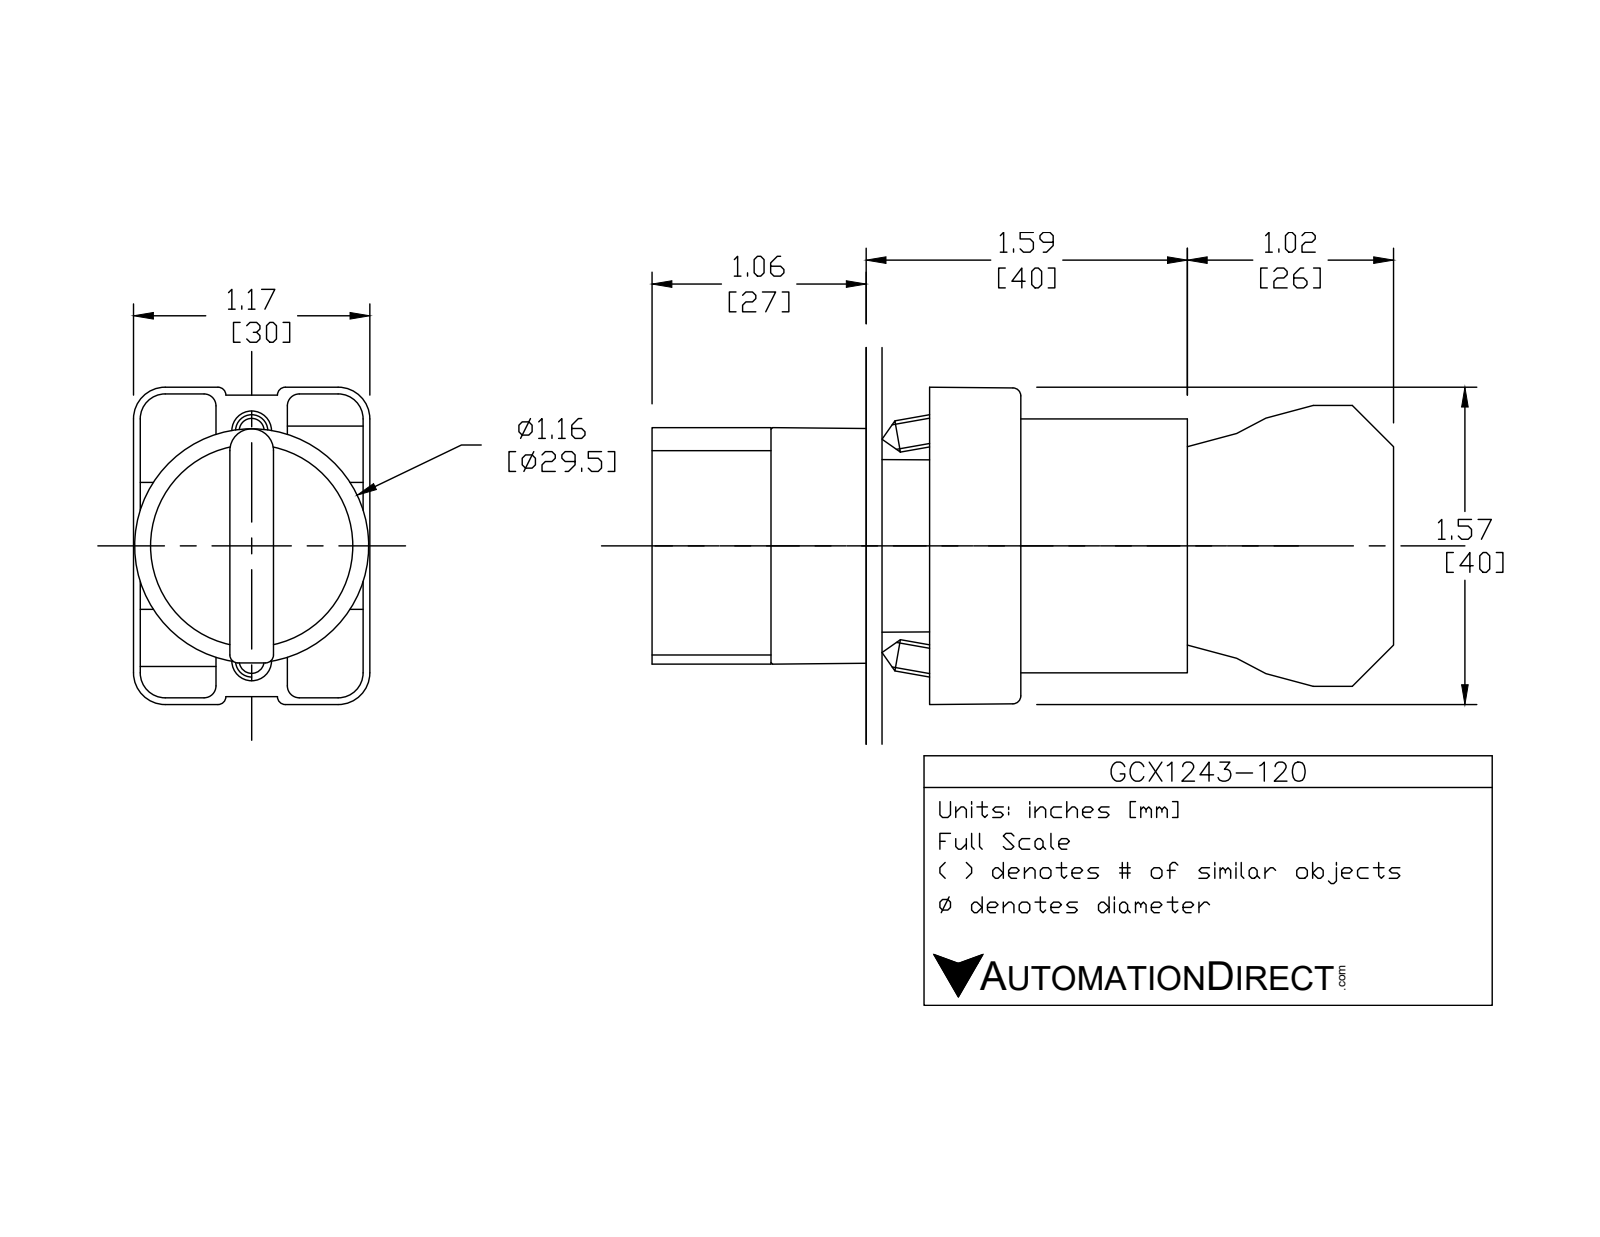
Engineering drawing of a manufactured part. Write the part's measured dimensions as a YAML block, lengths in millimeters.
part_name: "ecx1040; ecx1029; GCX1243-120; GCX1243 OPERATOR (+1 more)"
step_written_by: "SolidWorks 2016 (AUTOMOTIVE_DESIGN)"
units: millimeters
bodies: {solids: 8, faces: 445, planar: 263, cylindrical: 151, other: 31}
overall_size: [92.8, 40.2, 29.9]
volume: 45870
surface_area: 25160
round_holes:
  - {diameter: 2, count: 2}
  - {diameter: 3.1, count: 2}
  - {diameter: 3.3, count: 2}
  - {diameter: 2.2, count: 1}
  - {diameter: 5, count: 1}
  - {diameter: 11.9, count: 1}
  - {diameter: 22.3, count: 1}
  - {diameter: 22.6, count: 1}
  - {diameter: 26, count: 1}
round_bosses_or_shafts:
  - {diameter: 4, count: 4}
  - {diameter: 29.8, count: 1}
  - {diameter: 25.5, count: 1}
  - {diameter: 24, count: 1}
  - {diameter: 21.7, count: 1}
  - {diameter: 19.8, count: 1}
  - {diameter: 12.8, count: 1}
partial_cylinders:
  - {radius: 1.5, count: 24}
  - {radius: 1, count: 12}
  - {radius: 3.1, count: 12}
  - {radius: 4, count: 12}
  - {radius: 1, count: 9}
  - {radius: 3.3, count: 2}
  - {radius: 0.5, count: 1}
  - {radius: 1.6, count: 1}
face_to_face_distances: [21, 51.3, 30.3, 14.7, 31.6, 29.7, 12, 11.9, 0.8, 0.8]
hole_center_spacings: [6, 13.8, 12, 12.4]
